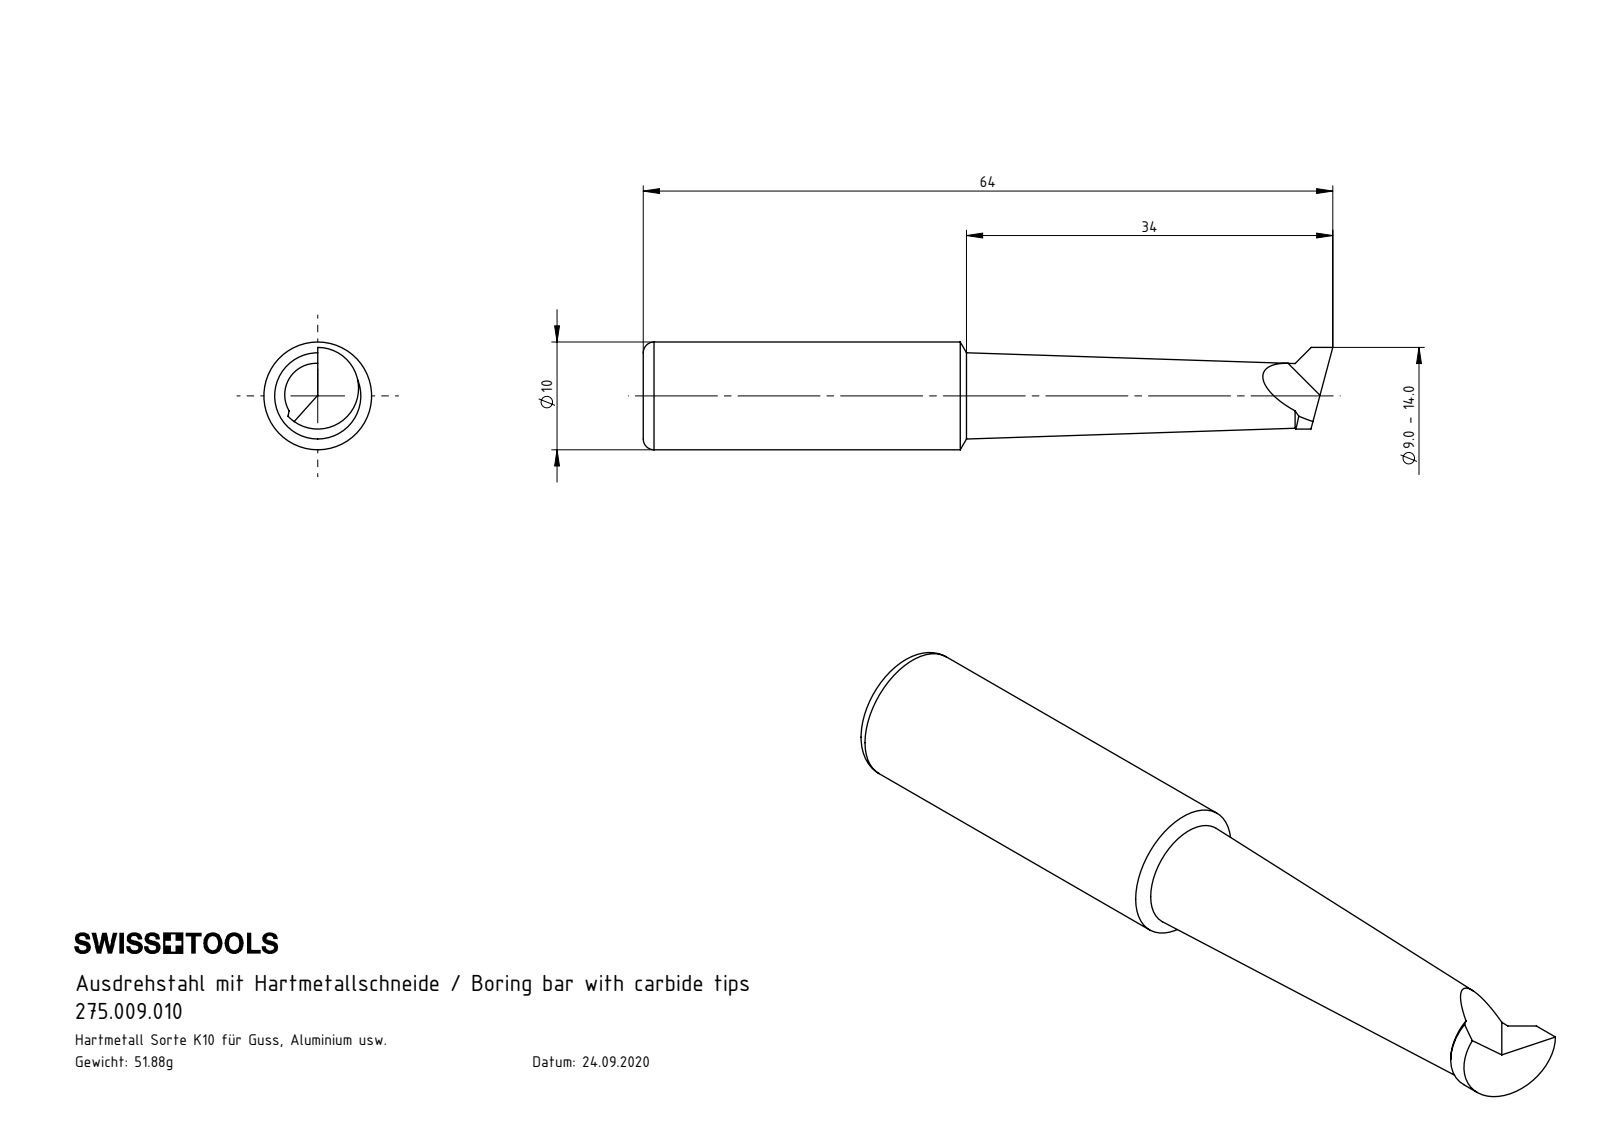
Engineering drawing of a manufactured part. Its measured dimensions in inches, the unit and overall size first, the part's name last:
Units: inches
Overall size (bounding box): 2.52 × 0.394 × 0.394
Round bosses / shafts (diameter × count): ⌀0.394 ×1
Partial cylindrical surfaces — rounded edges, fillets, slot ends (radius × count): R0.031 ×1
Volume: 0.221 in³ · Surface area: 2.801 in²
Bodies: 1 solid, 29 faces (3 planar, 3 cylindrical, 23 other)
Part name (STEP PRODUCT): U10.B09.001.034
STEP written by: SolidWorks 2012 (CONFIG_CONTROL_DESIGN)
